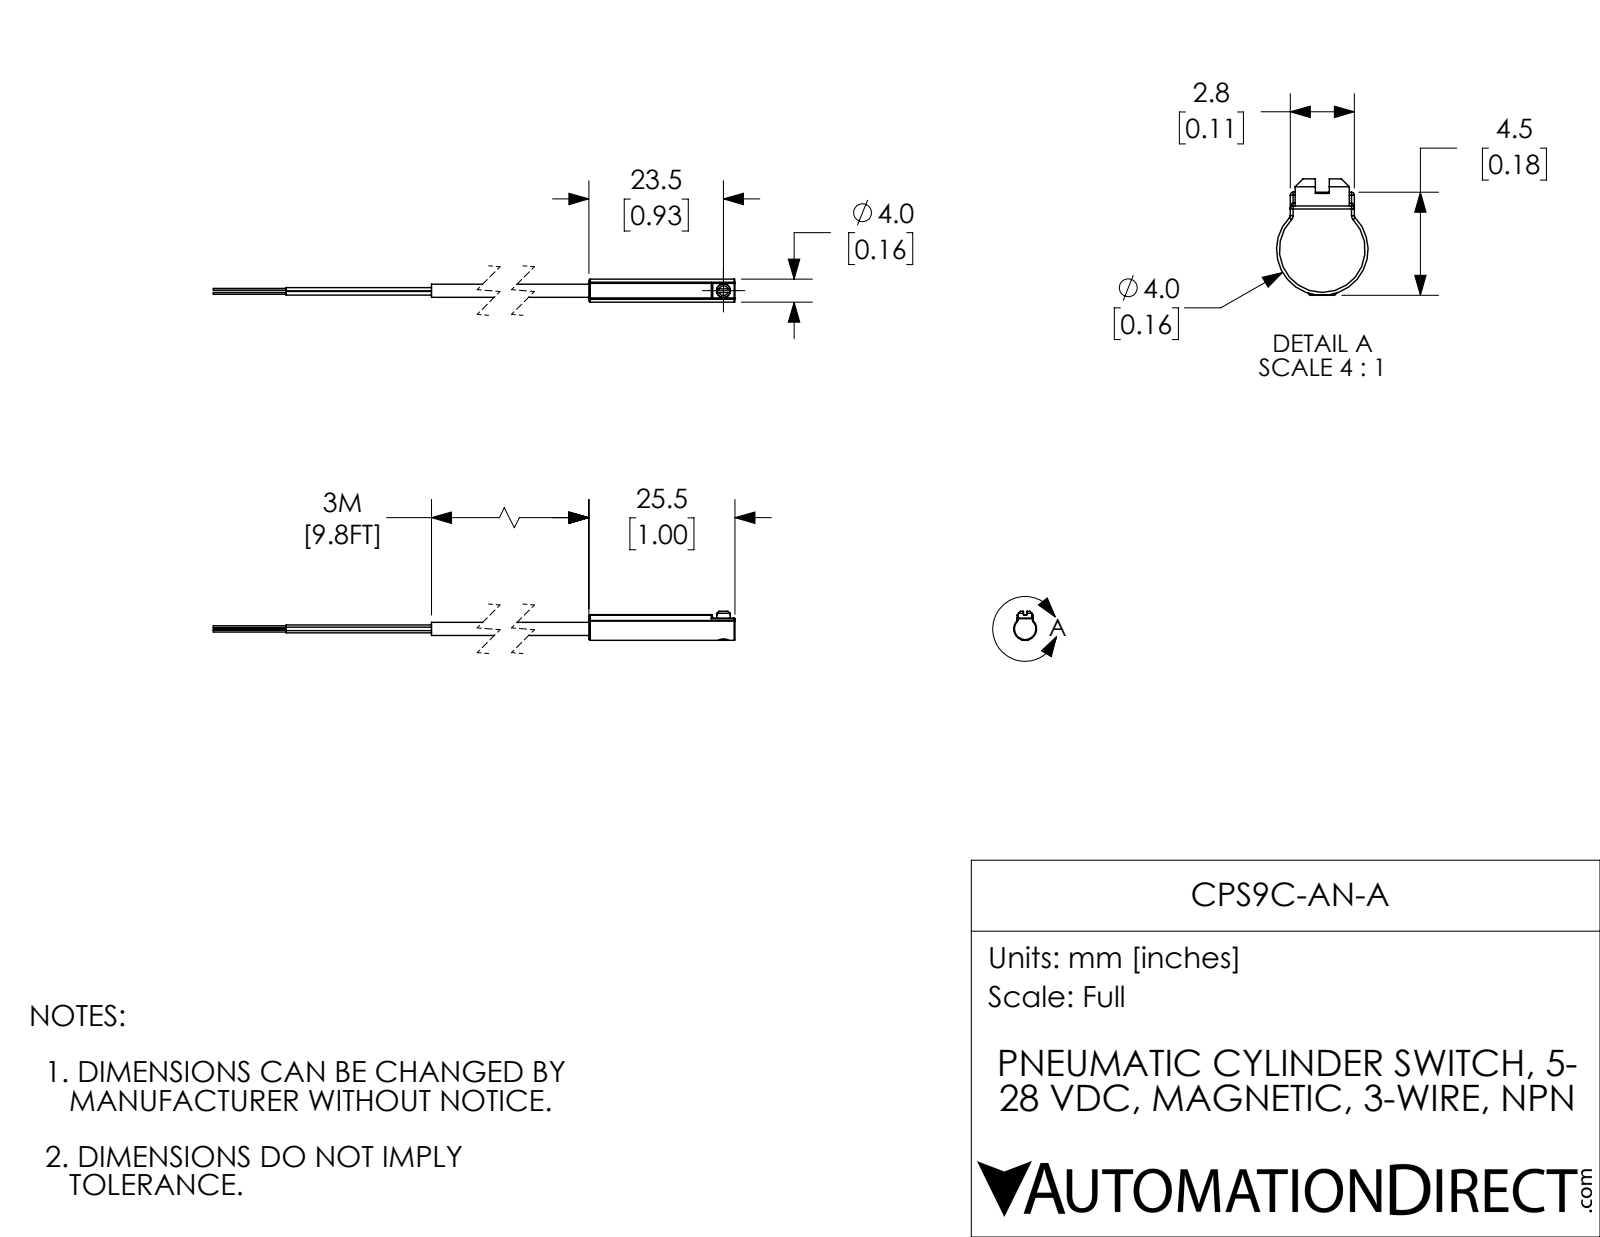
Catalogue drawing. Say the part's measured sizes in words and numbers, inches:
The part is named "CPS9C-AN-A". Its 3-D file was written by "SolidWorks 2019 (AUTOMOTIVE_DESIGN)". It is 2 solids with 84 faces: 20 planar, 37 cylindrical and 27 other. Overall it measures 6.689 by 0.2 by 0.157 inches. Its volume is 0.051 cubic inches and its surface area 2.16 square inches. Round holes: 1 of diameter 0.076. Round bosses or shafts: 3 of diameter 0.024, 3 of diameter 0.013, 1 of diameter 0.093, 1 of diameter 0.09. Partial cylindrical surfaces (rounded edges, fillets, slot ends): 13 of radius 0.005, 3 of radius 0.01, 1 of radius 0.079. The main face-to-face distances are 0.11, 1.004, 0.024, 5.189, 4.185, 0.043, 0.067, 0.022, 0.046, 0.025.
